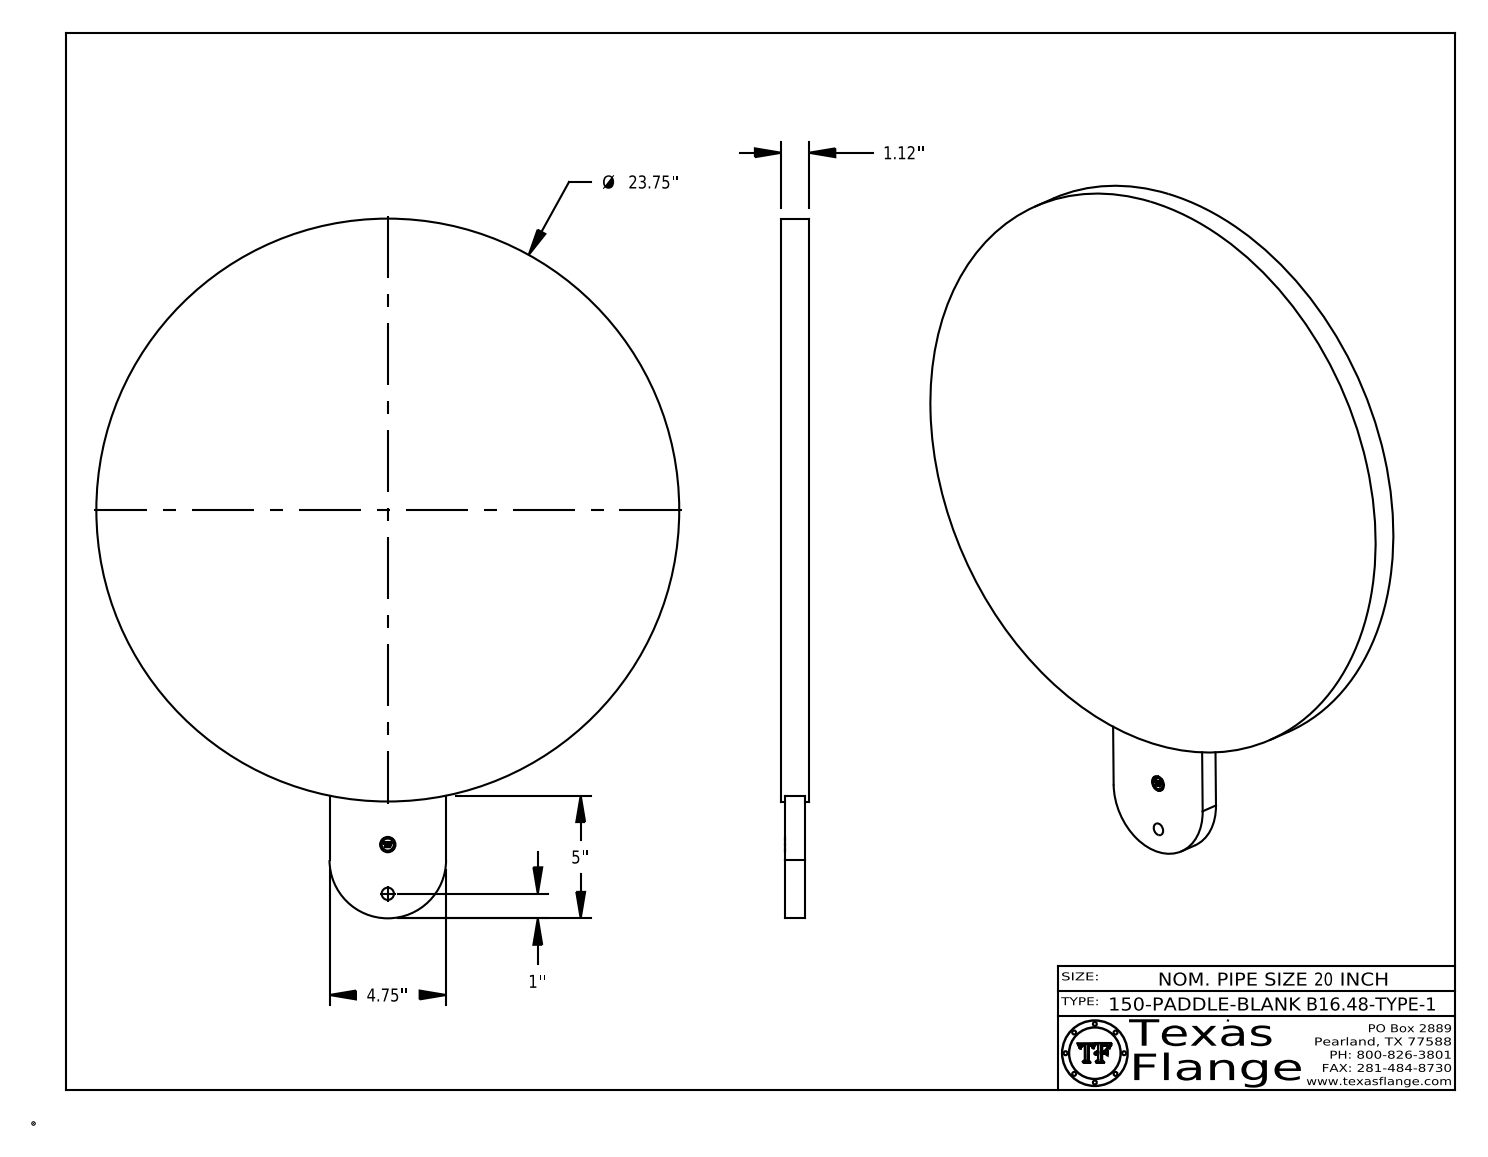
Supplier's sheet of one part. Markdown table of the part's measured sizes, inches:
| quantity | value |
| --- | --- |
| part name | 20-150-PADDLE-BLANK-B16.48-TYPE-1 |
| STEP written by | CATIA V5 STEP AP214 (AUTOMOTIVE_DESIGN) |
| units | inches |
| bodies | 1 solid, 396 faces (371 planar, 25 cylindrical, 0 other) |
| overall size | 28.51 × 23.75 × 1.12 |
| volume | 513.3 in³ |
| surface area | 1 018 in² |
| round holes (diameter × count) | 0.5 × 1, 0.625 × 1 |
| round bosses / shafts (diameter × count) | 0.038 × 8, 23.75 × 1, 0.492 × 1 |
| partial cylindrical surfaces (radius × count) | 2.375 × 1 |
| main face-to-face distances | 1.12, 0.14, 0.98, 0.84, 4.75, 0.155, 0.965, 0.825, 0.015, 2.313 |
| hole center spacings | 2.005 |
